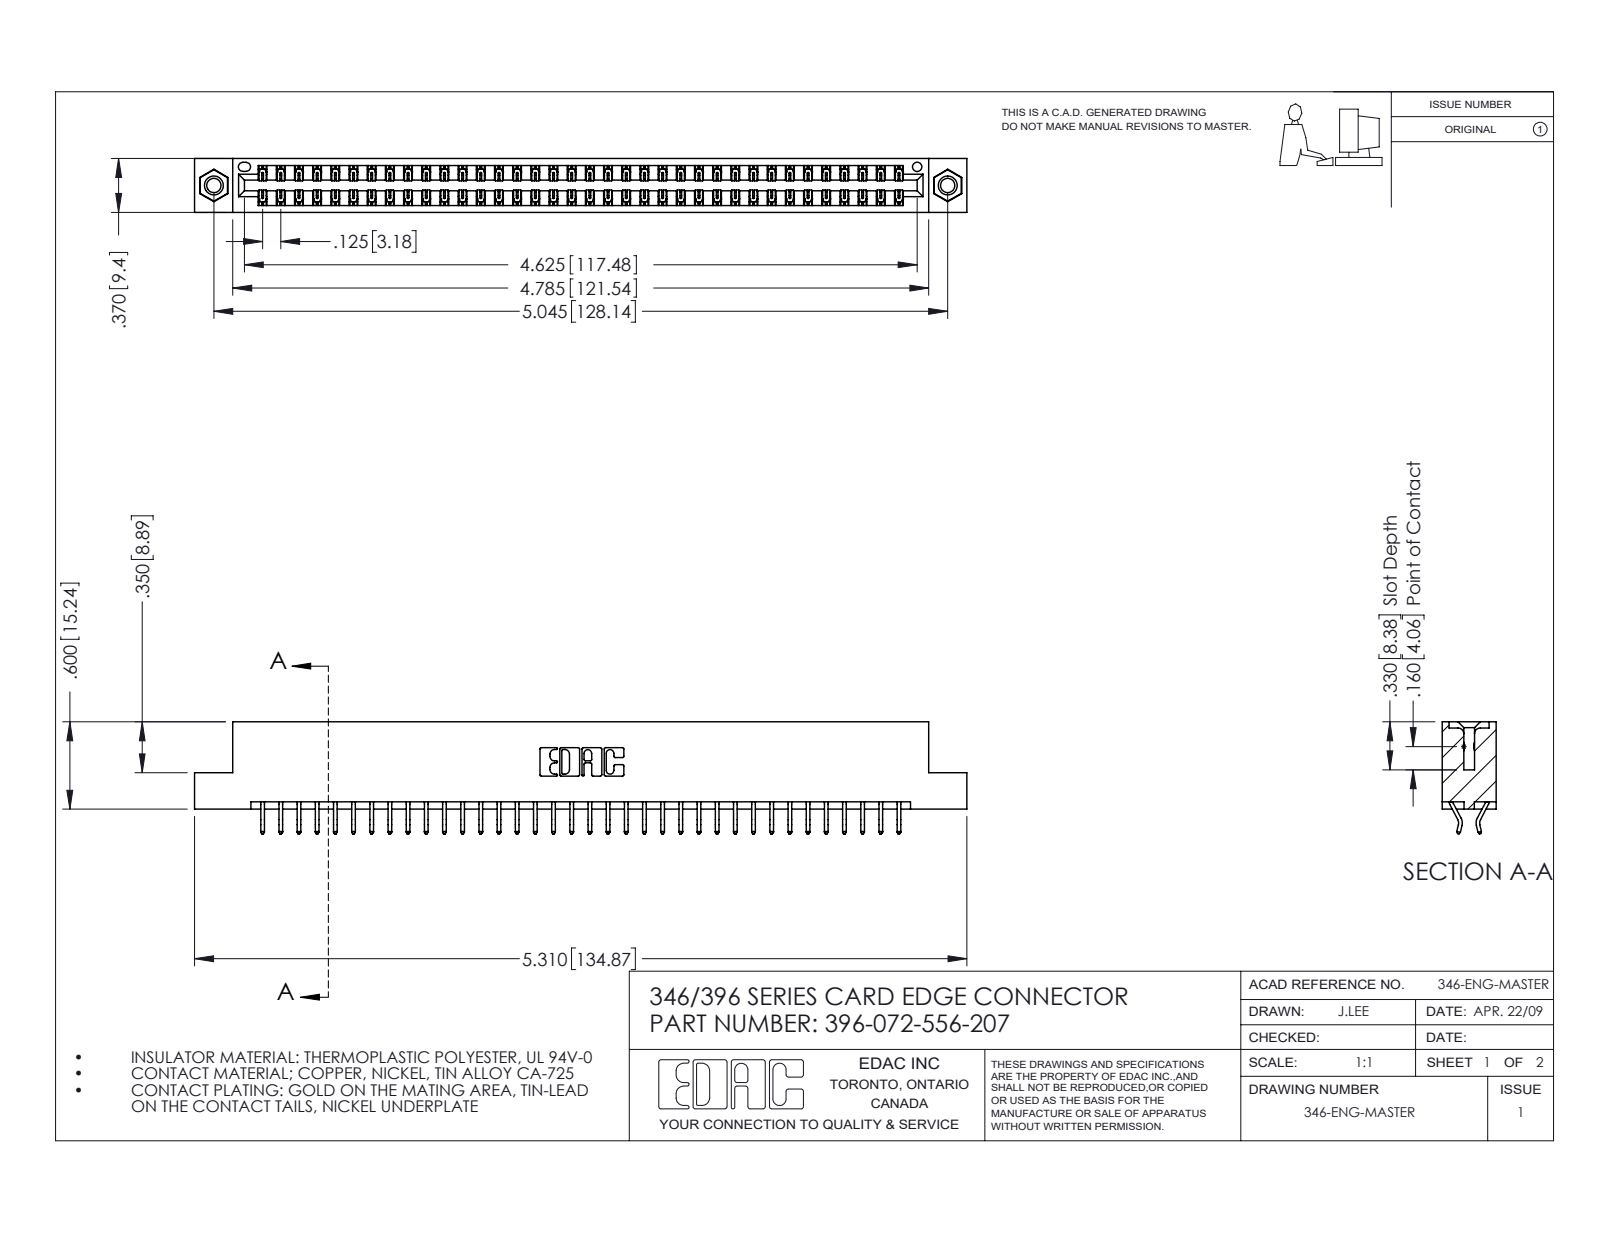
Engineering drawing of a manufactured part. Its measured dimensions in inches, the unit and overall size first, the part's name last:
Units: inches
Overall size (bounding box): 5.31 × 0.77 × 0.37
Round holes (diameter × count): ⌀0.098 ×2, ⌀0.125 ×2, ⌀0.156 ×2, ⌀0.064 ×1
Round bosses / shafts (diameter × count): ⌀0.155 ×2
Partial cylindrical surfaces — rounded edges, fillets, slot ends (radius × count): R0.006 ×108, R0.01 ×22, R0.007 ×6, R0.031 ×6, R0.026 ×3, R0.01 ×2, R0.014 ×2, R0.022 ×2
Main face-to-face distances: 0.048, 0.322, 0.37, 0.25, 0.025, 0.072, 0.298, 0.275, 0.148, 0.222
Hole centre spacings: 0.246, 4.836, 5.045
Volume: 0.799 in³ · Surface area: 27.69 in²
Bodies: 75 solids, 4358 faces (2916 planar, 1426 cylindrical, 16 other)
Part name (STEP PRODUCT): 345-250-001_345-250-005-103; 346 Part_Flush Mounting Lugs - 0.156 Dia-TI; 345-292-001_556 Tail; 396-072-556-207
STEP written by: SolidWorks 2016 (CONFIG_CONTROL_DESIGN)
